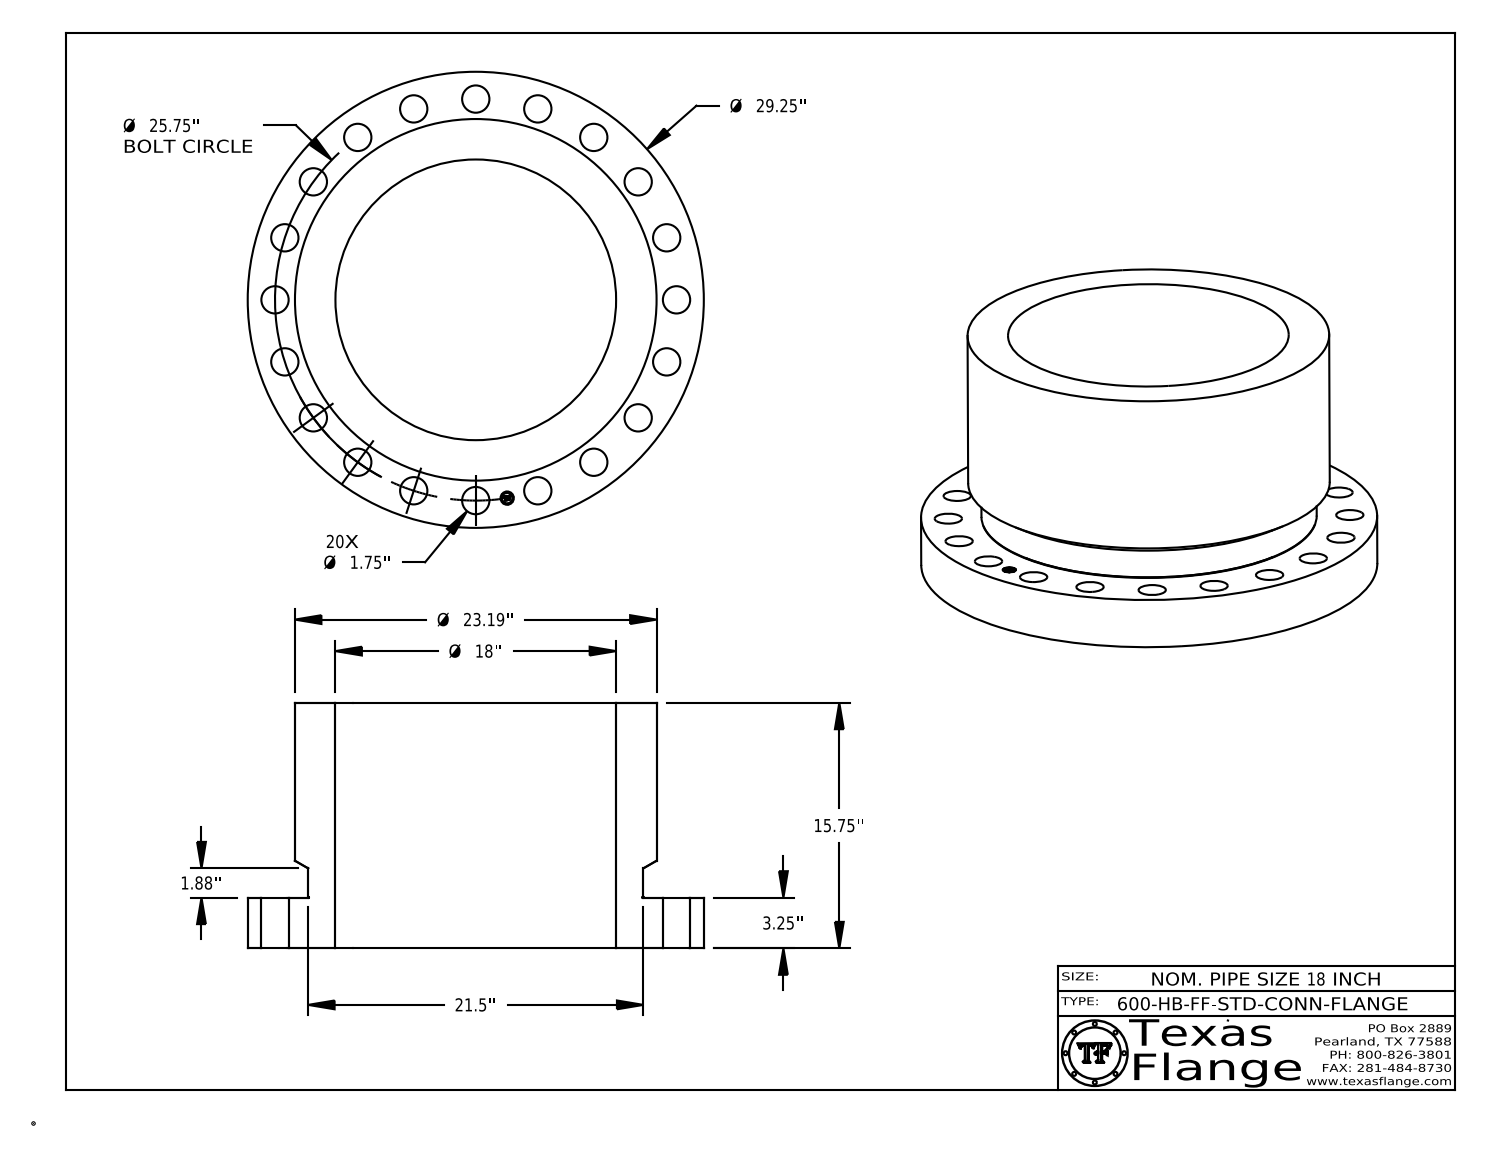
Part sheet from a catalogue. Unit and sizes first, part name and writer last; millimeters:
Units: millimetres
Overall size (bounding box): 743 × 743 × 400.1
Round holes (diameter × count): ⌀44.5 ×20, ⌀21.6 ×1, ⌀457.2 ×1
Round bosses / shafts (diameter × count): ⌀1.3 ×8, ⌀743 ×1, ⌀589 ×1, ⌀546.1 ×1, ⌀17 ×1
Main face-to-face distances: 82.6, 400.1, 317.5, 82.4, 317.6, 6.5, 6.3, 1.2, 4.2, 5.4
Hole centre spacings: 327, 622, 646, 202.1, 297, 102.3, 384.4, 462.5
Volume: 52 000 000 mm³ · Surface area: 2 117 000 mm²
Bodies: 1 solid, 442 faces (368 planar, 68 cylindrical, 6 other)
Part name (STEP PRODUCT): 18-600-HB-FF-STD-CONN-FLANGE
STEP written by: CATIA V5 STEP AP214 (AUTOMOTIVE_DESIGN)
